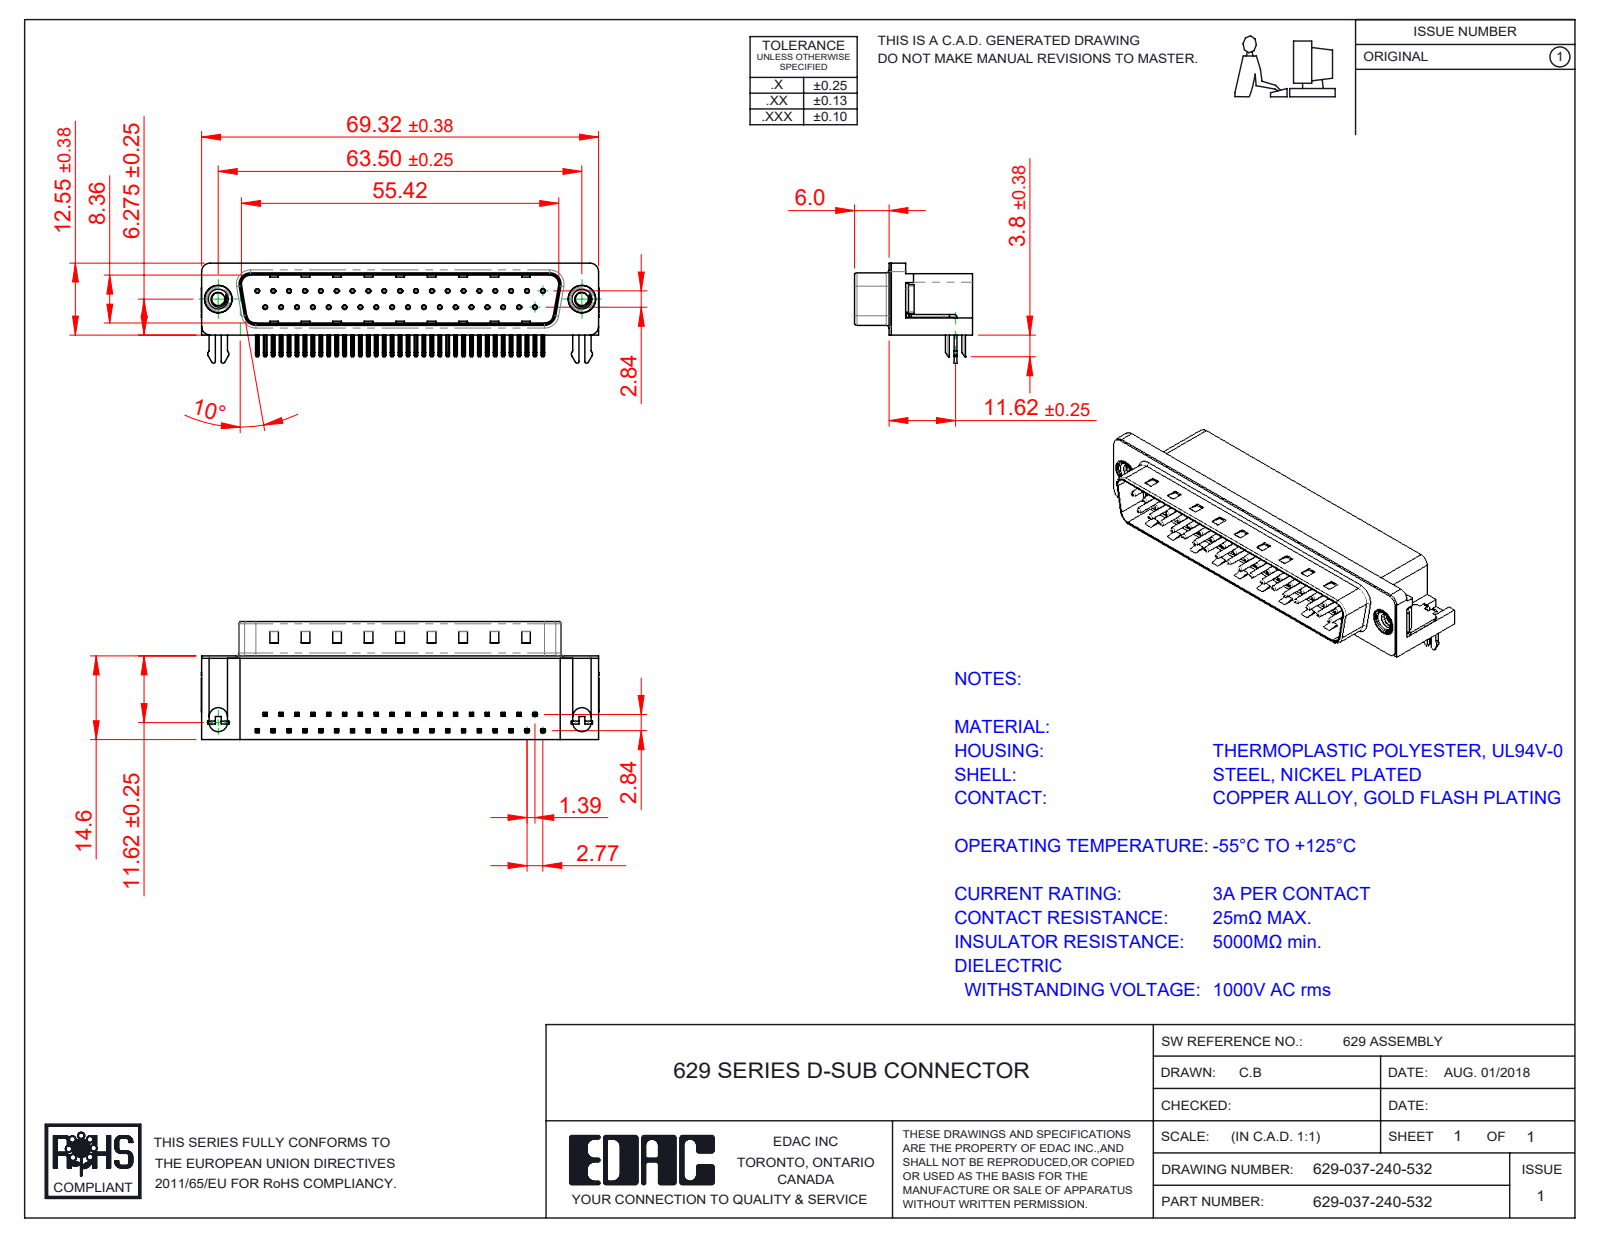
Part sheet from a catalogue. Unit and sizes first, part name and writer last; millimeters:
Units: millimetres
Overall size (bounding box): 69.4 × 20.6 × 17.48
Round holes (diameter × count): ⌀0.35 ×37, ⌀0.8 ×37, ⌀2.26 ×2, ⌀4 ×2, ⌀4.8 ×2, ⌀5 ×2
Round bosses / shafts (diameter × count): ⌀0.75 ×37, ⌀4.9 ×2, ⌀4.75 ×2, ⌀3.9 ×2
Partial cylindrical surfaces — rounded edges, fillets, slot ends (radius × count): R0.25 ×156, R0.12 ×74, R1 ×16, R0.5 ×14, R1.6 ×8, R1.5 ×7, R0.32 ×4, R0.9 ×4
Main face-to-face distances: 0.4, 10.35, 14.2, 8.76, 2.1, 1.7, 10.46, 10.86, 14.6, 1.35
Hole centre spacings: 2.77, 3.16, 5.54, 8.31, 11.08, 13.85, 16.62, 19.39
Volume: 9 971 mm³ · Surface area: 10 831 mm²
Bodies: 43 solids, 3237 faces (2043 planar, 923 cylindrical, 271 other)
Part name (STEP PRODUCT): 629 2 Prong Board Lock; 629 Contact Bottom; 629 Contact Top; 629 4-40 Threaded Rivet (+3 more)
STEP written by: SolidWorks 2020 (CONFIG_CONTROL_DESIGN)
